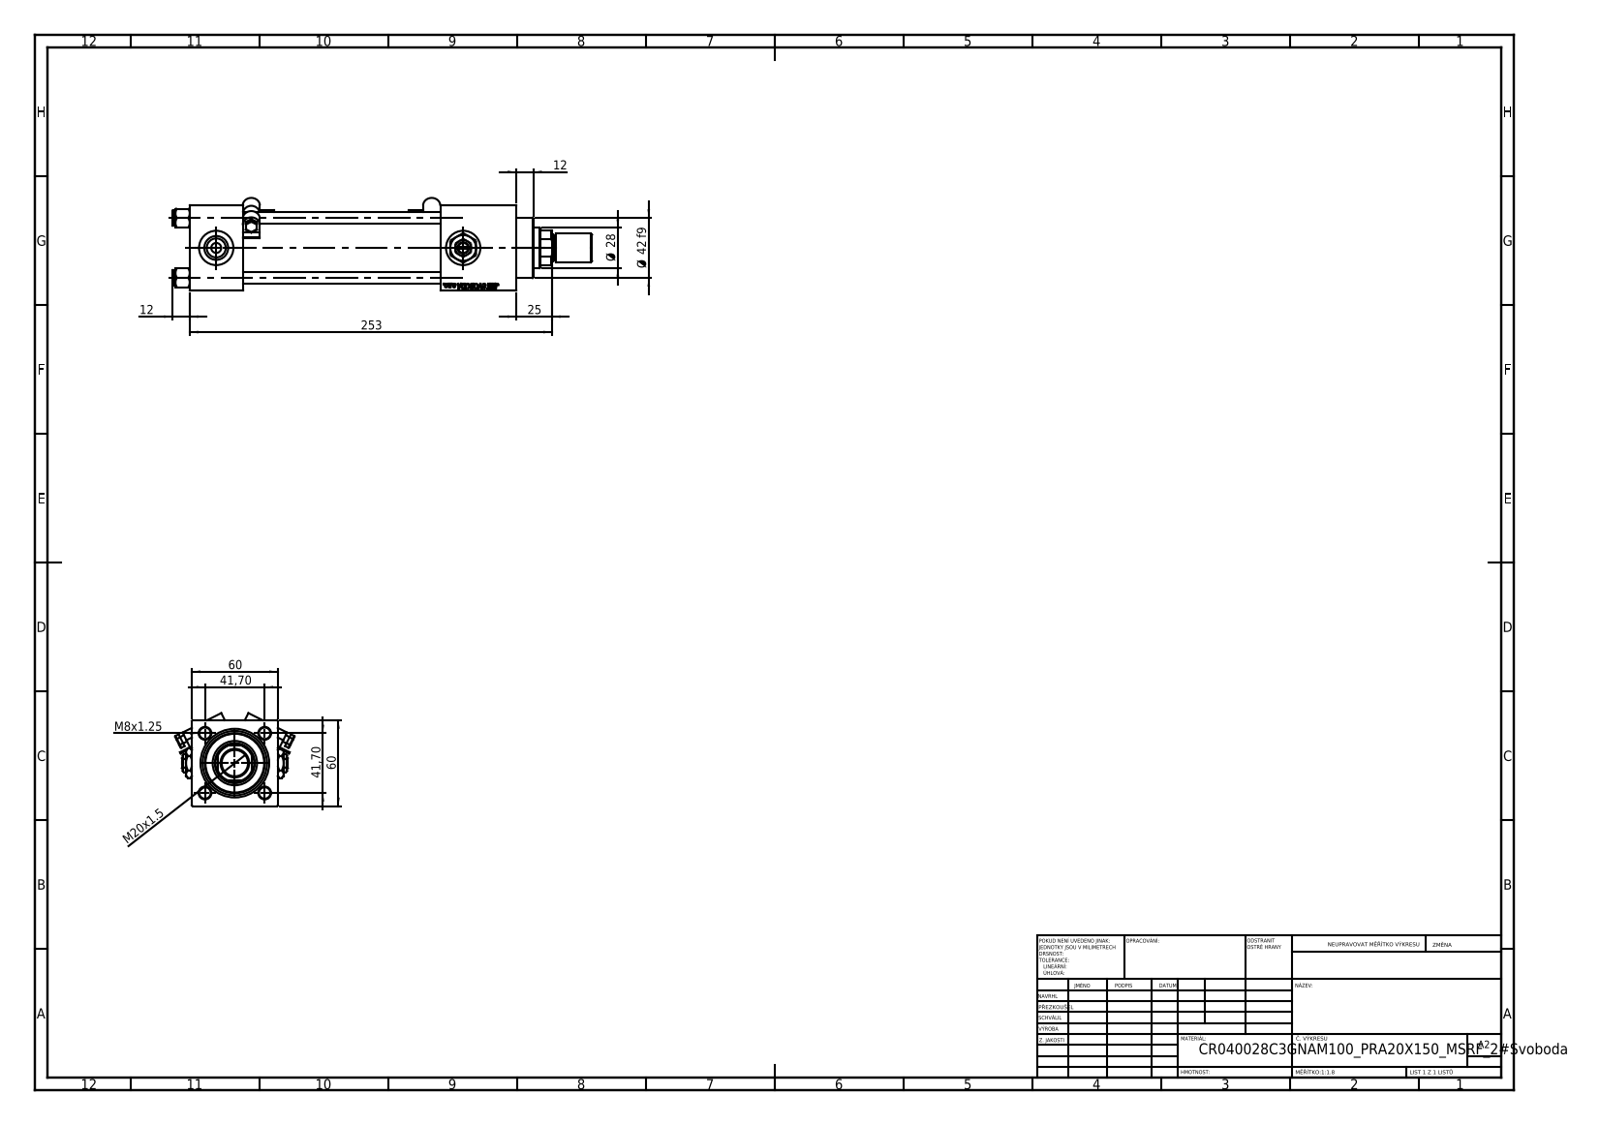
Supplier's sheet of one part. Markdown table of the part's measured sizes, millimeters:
| quantity | value |
| --- | --- |
| part name | Zatka_pro_OIL_PORT; ROD_END_AH; MSRF_MSRG1; NUT_M5_C (+4 more) |
| STEP written by | SolidWorks 2019 (CONFIG_CONTROL_DESIGN) |
| units | millimeters |
| bodies | 16 solids, 1328 faces (614 planar, 130 cylindrical, 584 other) |
| overall size | 293 × 83.44 × 64.97 |
| volume | 534 430 mm³ |
| surface area | 157 771 mm² |
| round holes (diameter × count) | 8 × 4, 7 × 2, 16.66 × 2, 24 × 2, 18.5 × 1, 28 × 1, 31 × 1, 40 × 1, 45 × 1 |
| round bosses / shafts (diameter × count) | 11 × 4, 5 × 2, 2.5 × 2, 46 × 1, 42 × 1, 20 × 1, 18 × 1 |
| partial cylindrical surfaces (radius × count) | 0.5 × 12, 6 × 4, 13.5 × 1 |
| main face-to-face distances | 60, 37, 175, 138, 53, 191, 199.3, 162.3, 24.3, 228 |
| hole center spacings | 29.49, 41.7, 58.97, 172.5 |
